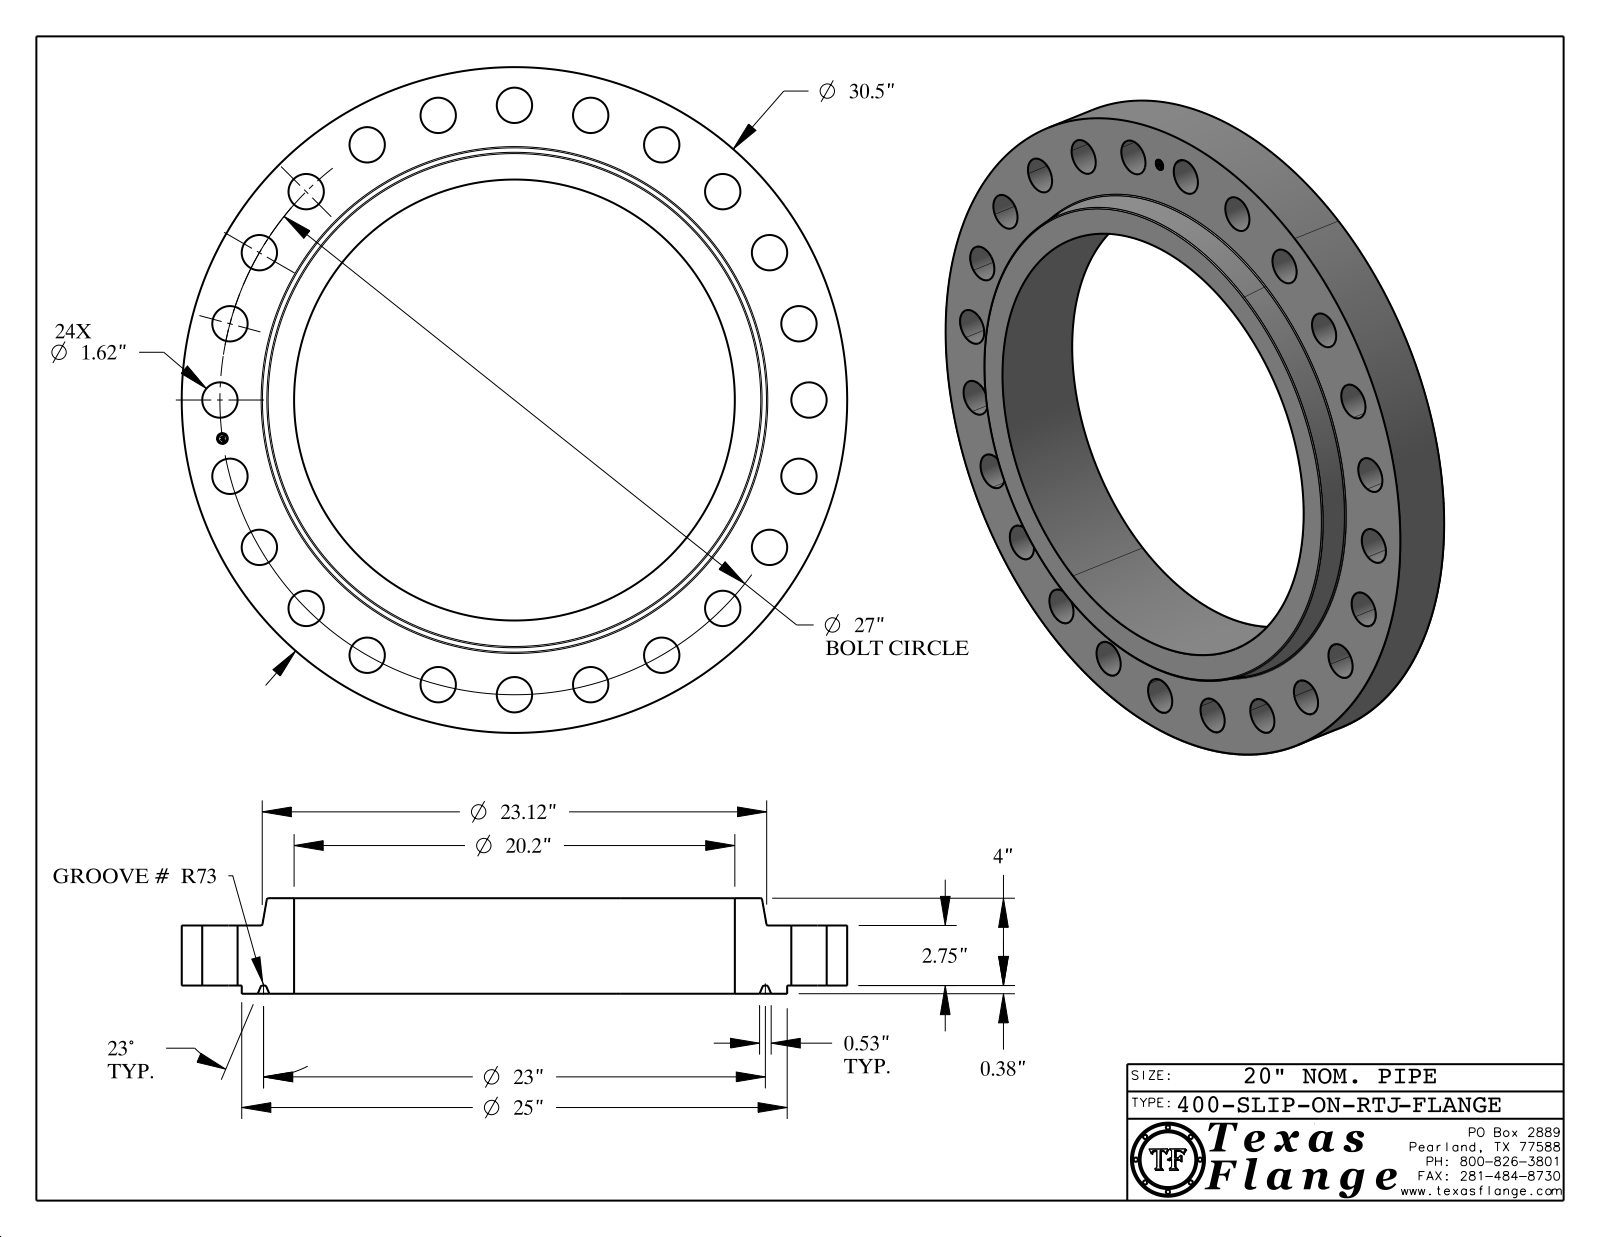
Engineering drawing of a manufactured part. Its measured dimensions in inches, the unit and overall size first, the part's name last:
Units: inches
Overall size (bounding box): 30.5 × 30.5 × 4.375
Round holes (diameter × count): ⌀1.62 ×24, ⌀0.495 ×1, ⌀20.2 ×1
Round bosses / shafts (diameter × count): ⌀0.03 ×8, ⌀30.5 ×1, ⌀25 ×1, ⌀0.39 ×1
Main face-to-face distances: 2.75, 0.375, 3.125, 4.375, 4, 1.25, 3.11, 2.735, 0.015, 1.265
Hole centre spacings: 13.5, 3.524, 6.988, 10.333, 16.437, 24.945, 26.769, 21.421
Volume: 1 160 in³ · Surface area: 1 735 in²
Bodies: 1 solid, 459 faces (371 planar, 74 cylindrical, 14 other)
Part name (STEP PRODUCT): 400-SLIP-ON-RTJ
STEP written by: CATIA V5 STEP AP214 (AUTOMOTIVE_DESIGN)
